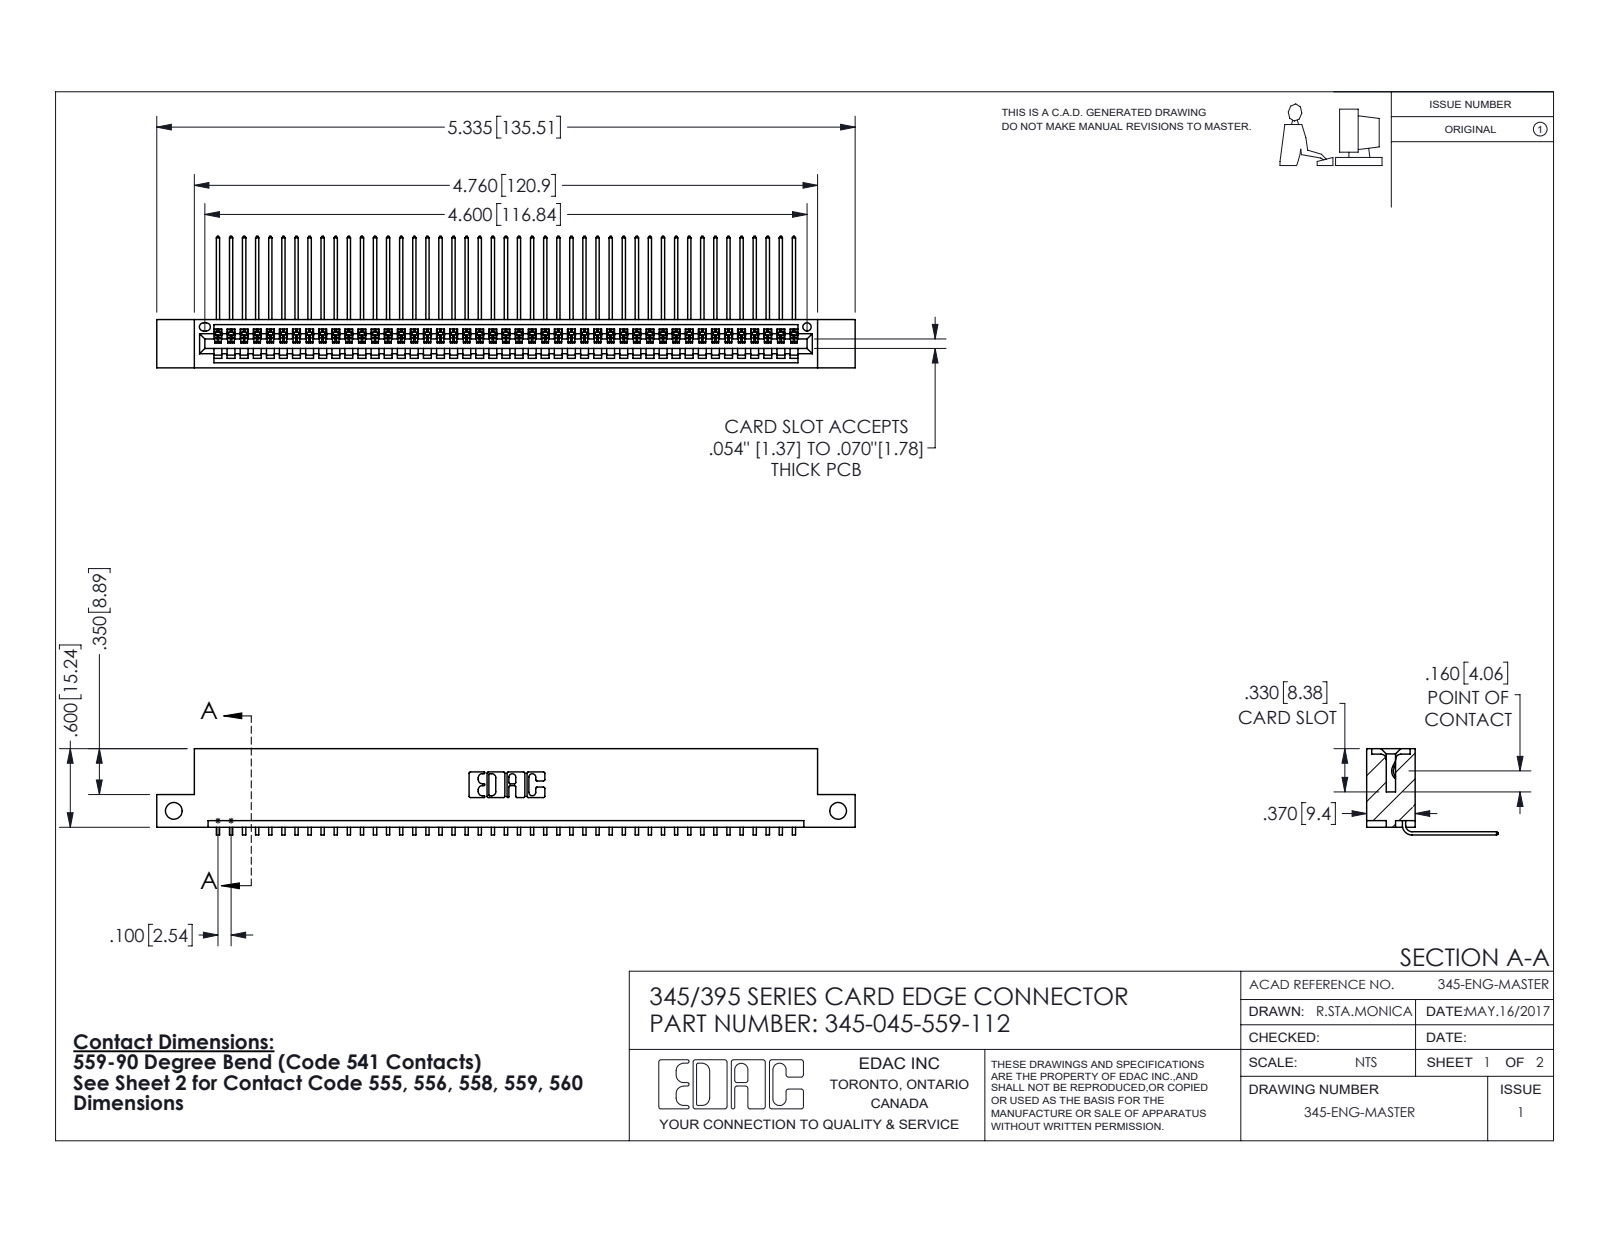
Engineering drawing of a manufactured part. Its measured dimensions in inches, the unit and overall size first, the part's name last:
Units: inches
Overall size (bounding box): 5.335 × 1.005 × 0.659
Round holes (diameter × count): ⌀0.128 ×2, ⌀0.064 ×1
Partial cylindrical surfaces — rounded edges, fillets, slot ends (radius × count): R0.006 ×90, R0.01 ×22, R0.007 ×6, R0.031 ×6, R0.026 ×3, R0.031 ×2, R0.04 ×2, R0.014 ×1
Main face-to-face distances: 0.298, 0.072, 0.37, 0.2, 0.098, 0.272, 0.025, 0.225, 0.149, 0.072
Hole centre spacings: 5.075
Volume: 0.791 in³ · Surface area: 27.9 in²
Bodies: 46 solids, 2826 faces (1970 planar, 856 cylindrical, 0 other)
Part name (STEP PRODUCT): 345 Part_Flush Mounting Lugs - Side Mount; 345-045-559-112; 345-292-001_558 559 Tail - 1
STEP written by: SolidWorks 2016 (CONFIG_CONTROL_DESIGN)
